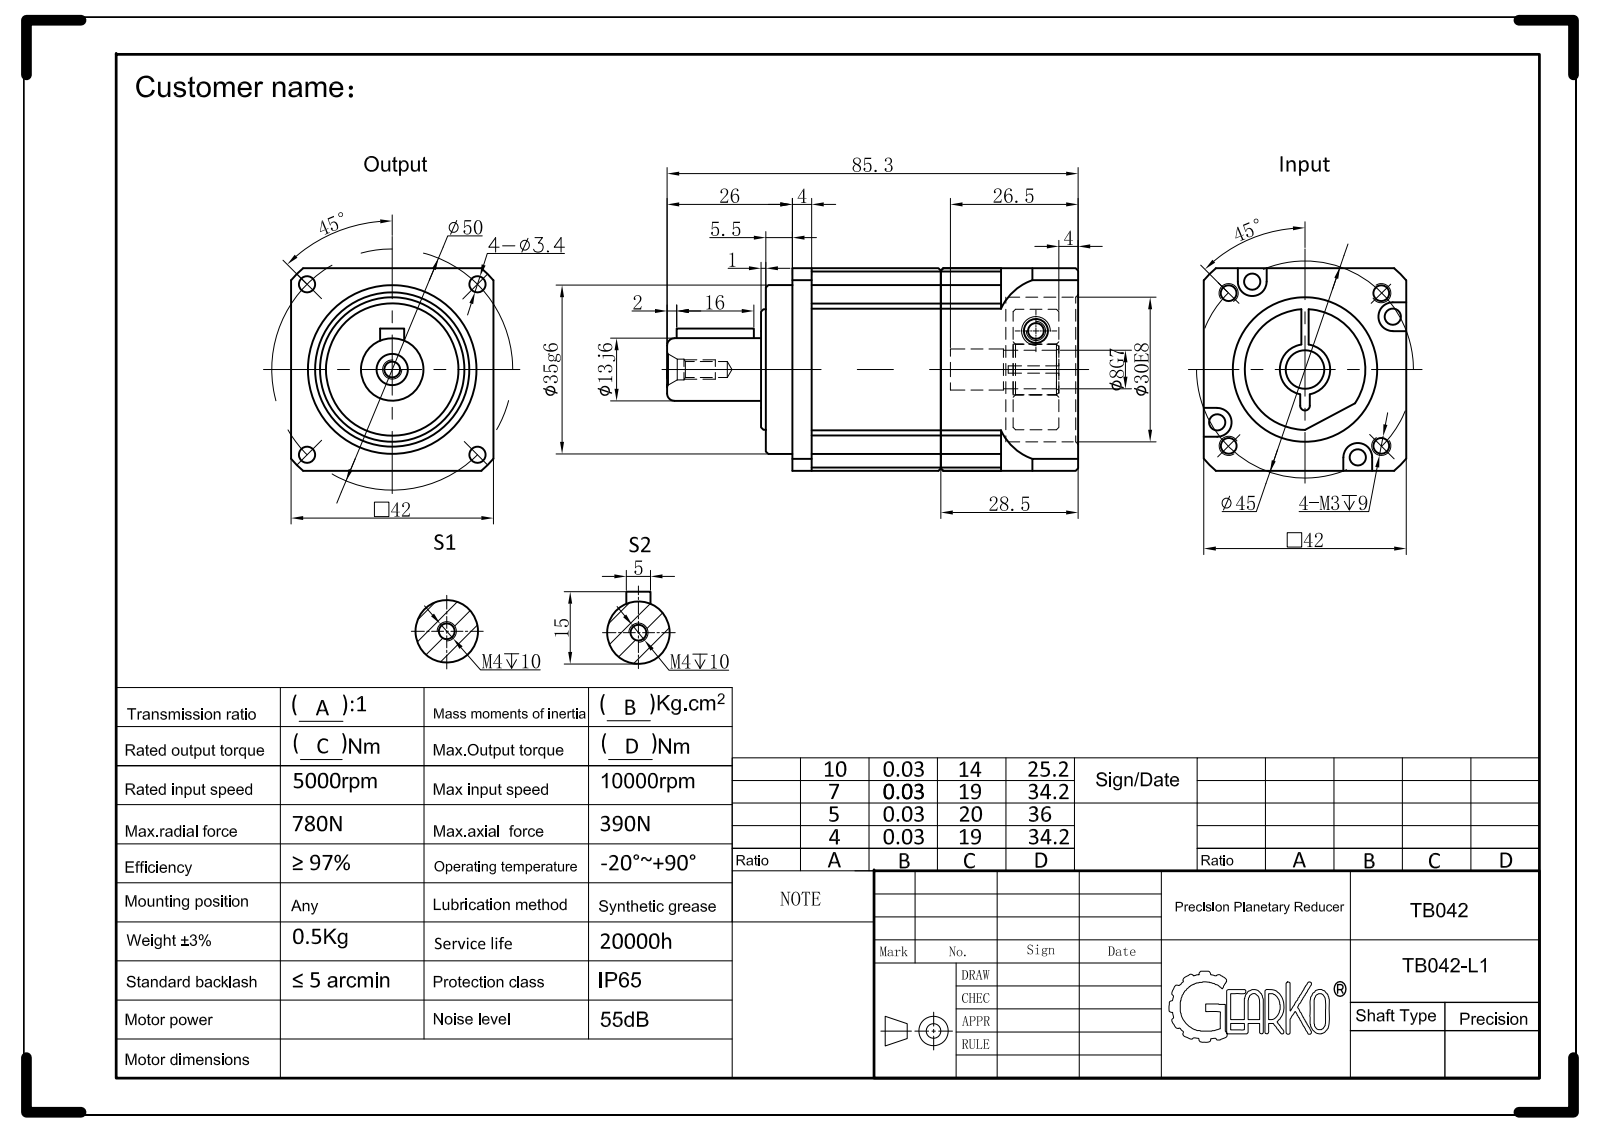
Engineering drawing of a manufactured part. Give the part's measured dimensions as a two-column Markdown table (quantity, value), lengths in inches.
| quantity | value |
| --- | --- |
| part name | CQA-001; TB042-L1-8-30-45-M3-26-3.5; JJT-001; CZA-001-8 (+1 more) |
| STEP written by | SolidWorks 2017 (CONFIG_CONTROL_DESIGN) |
| units | inches |
| bodies | 5 solids, 351 faces (136 planar, 127 cylindrical, 88 other) |
| overall size | 3.358 × 1.654 × 1.654 |
| volume | 5.676 in³ |
| surface area | 42.69 in² |
| round holes (diameter × count) | 0.134 × 8, 0.094 × 4, 0.063 × 1, 0.13 × 1, 0.157 × 1, 0.169 × 1, 0.177 × 1, 0.205 × 1, 0.303 × 1, 0.315 × 1, 0.335 × 1, 0.413 × 1 |
| round bosses / shafts (diameter × count) | 1.378 × 1, 0.985 × 1, 0.669 × 1, 0.63 × 1, 0.591 × 1, 0.571 × 1, 0.563 × 1, 0.551 × 1 |
| partial cylindrical surfaces (radius × count) | 0.157 × 6, 0.118 × 4, 0.098 × 2, 0.039 × 1, 0.965 × 1, 1.102 × 1 |
| main face-to-face distances | 1.654, 1.429, 0.217, 1.213, 2.551, 2.335, 1.122, 0.288, 1.365, 0.157 |
| hole center spacings | 1.324, 0.098, 0.886, 0.984, 1.183, 1.253, 1.87, 0.266 |
